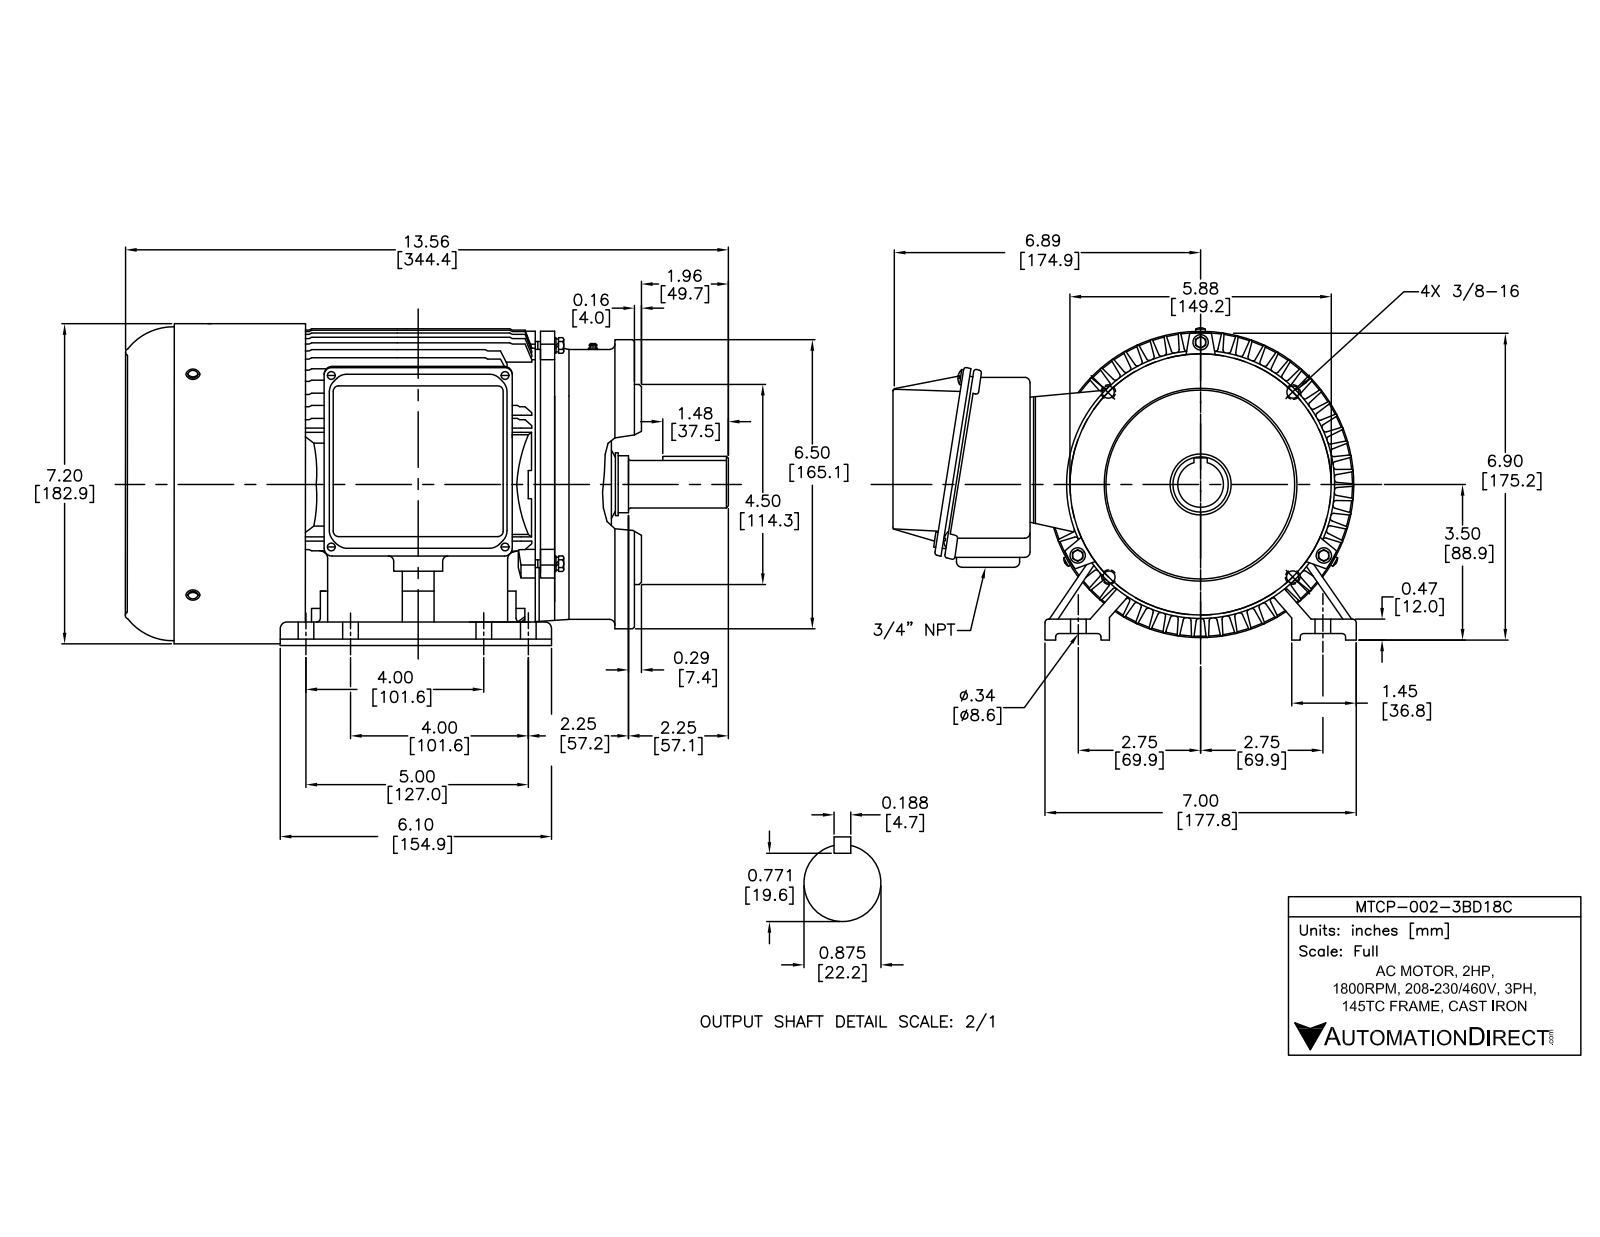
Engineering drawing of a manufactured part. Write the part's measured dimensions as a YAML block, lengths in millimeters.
part_name: "hex head bolts-full thread grade c gb_GB_FASTENER_BOLT_HHBFTC M5X10-N; spring lock washers--normal type gb_GB_FASTENER_WASHER_SW 6; spring lock washers--normal type gb_GB_FASTENER_WASHER_SW 5; hex head bolts-full thread grade c gb_GB_FASTENER_BOLT_HHBFTC M6X35-N (+5 more)"
step_written_by: "SolidWorks 2017 (AUTOMOTIVE_DESIGN)"
units: millimeters
bodies: {solids: 47, faces: 2399, planar: 667, cylindrical: 963, other: 769}
overall_size: [386.55, 246.78, 182.39]
volume: 2069000
surface_area: 760350
round_holes:
  - {diameter: 5.8, count: 14}
  - {diameter: 9, count: 12}
  - {diameter: 4.2, count: 11}
  - {diameter: 7.94, count: 4}
  - {diameter: 5, count: 3}
  - {diameter: 5.3, count: 3}
  - {diameter: 5.4, count: 3}
  - {diameter: 6.4, count: 3}
  - {diameter: 6.68, count: 3}
  - {diameter: 7, count: 3}
  - {diameter: 7.69, count: 3}
  - {diameter: 2, count: 2}
round_bosses_or_shafts:
  - {diameter: 5, count: 11}
  - {diameter: 12, count: 3}
  - {diameter: 10, count: 3}
  - {diameter: 9.88, count: 3}
  - {diameter: 8, count: 3}
  - {diameter: 6, count: 3}
  - {diameter: 175.4, count: 1}
  - {diameter: 173, count: 1}
partial_cylinders:
  - {radius: 0.5, count: 176}
  - {radius: 1, count: 67}
  - {radius: 2, count: 54}
  - {radius: 1.25, count: 27}
  - {radius: 7, count: 24}
  - {radius: 0.34, count: 16}
  - {radius: 3, count: 15}
  - {radius: 0.5, count: 14}
face_to_face_distances: [4, 1.2, 12, 2, 6, 329.4, 328.2, 65.05, 63.85, 264.35]
hole_center_spacings: [54, 139.7, 90, 25.4, 35, 60.4, 74.61, 76.2]
